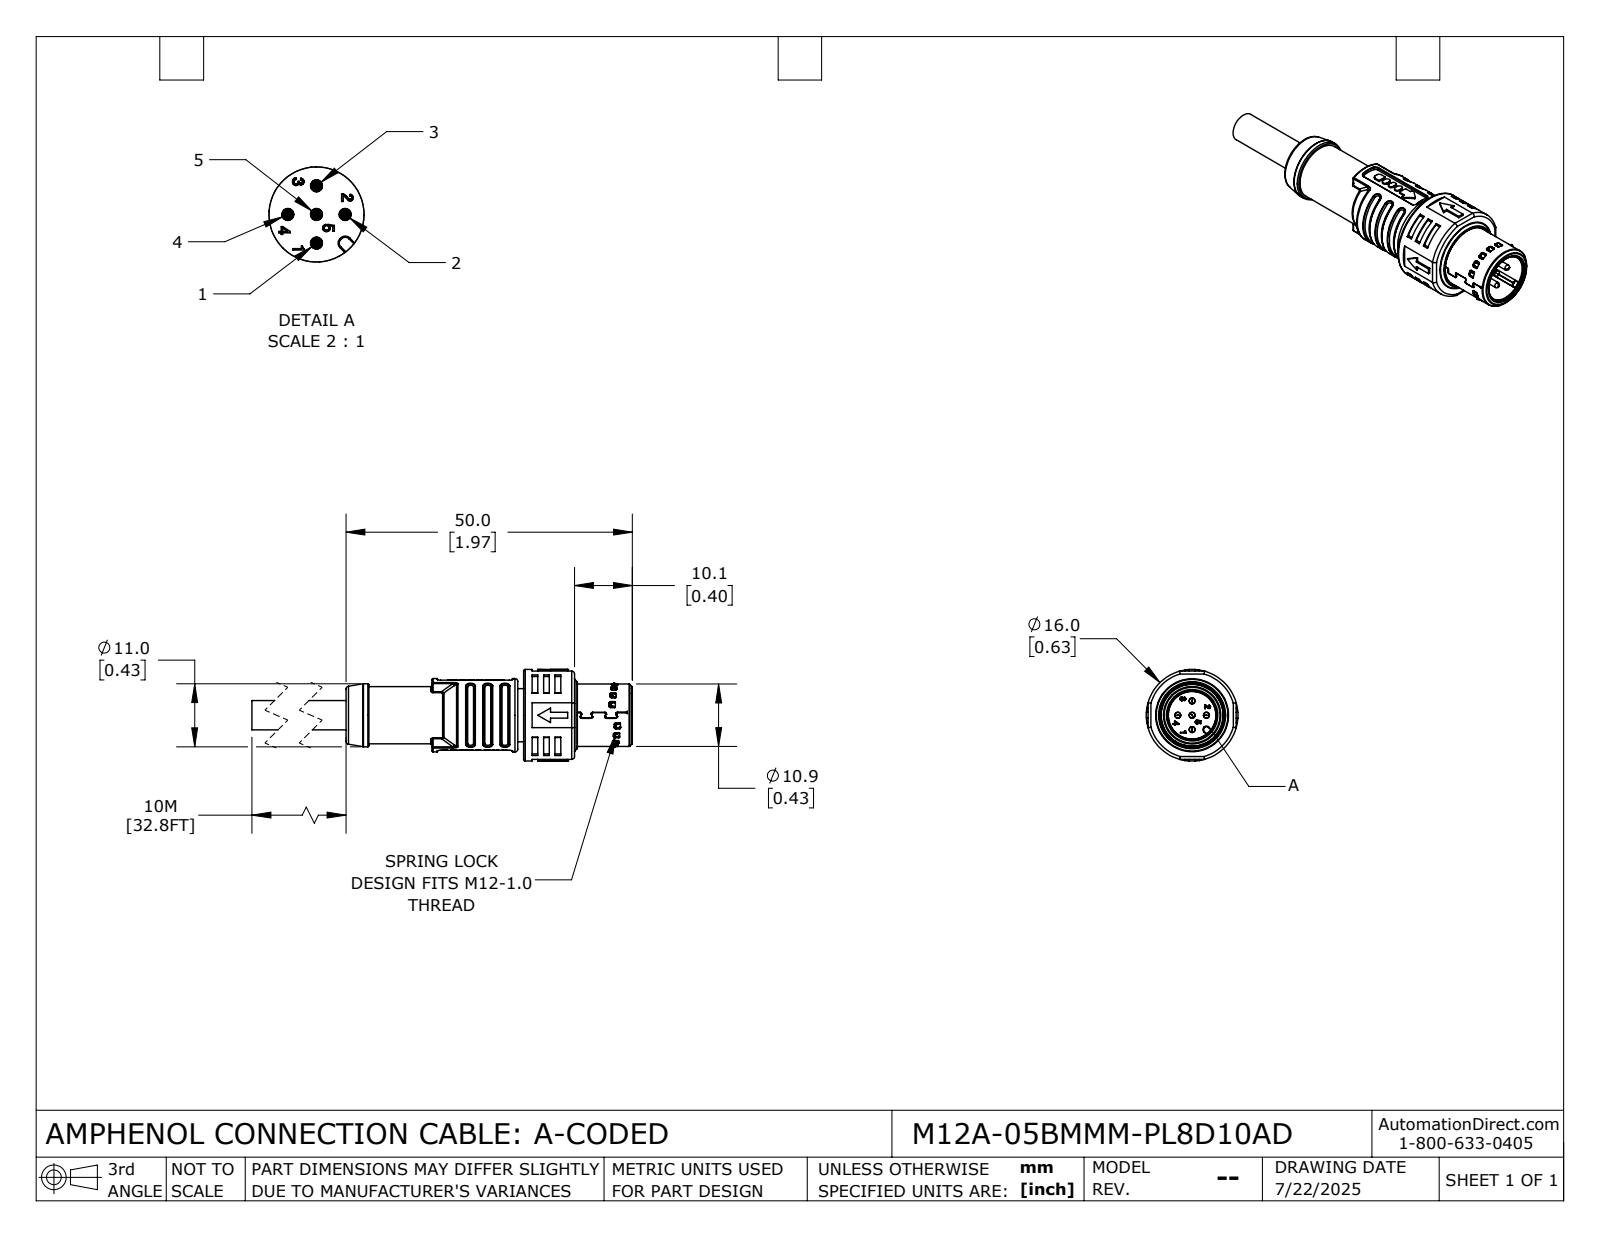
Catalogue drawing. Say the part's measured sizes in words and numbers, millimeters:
The part is named "M12A-05BMMM-PL8D10AD". Its 3-D file was written by "SolidWorks 2024 (CONFIG_CONTROL_DESIGN)". It is 1 solid with 2230 faces: 1085 planar, 648 cylindrical and 497 other. Overall it measures 65 by 16 by 16 millimeters. Its volume is 5 076 cubic millimeters and its surface area 5 586 square millimeters. Round holes: 5 of diameter 1.05, 1 of diameter 8.3, 1 of diameter 9, 1 of diameter 10.15, 1 of diameter 10.5, 1 of diameter 10.9, 1 of diameter 11.5, 1 of diameter 11.8, 1 of diameter 14.2. Round bosses or shafts: 5 of diameter 1, 1 of diameter 16, 1 of diameter 14.1, 1 of diameter 12.8, 1 of diameter 12.4, 1 of diameter 11, 1 of diameter 10.45, 1 of diameter 10.4. Partial cylindrical surfaces (rounded edges, fillets, slot ends): 114 of radius 0.2, 66 of radius 0.25, 64 of radius 0.3, 44 of radius 0.15, 38 of radius 0.5, 12 of radius 0.13, 11 of radius 0.7, 10 of radius 0.1. The main face-to-face distances are 1, 10.1, 8.9, 8.6, 2.5, 30, 1.5, 1.2, 32.5, 15.4. The hole center spacings are 2.5, 3.54, 5.
